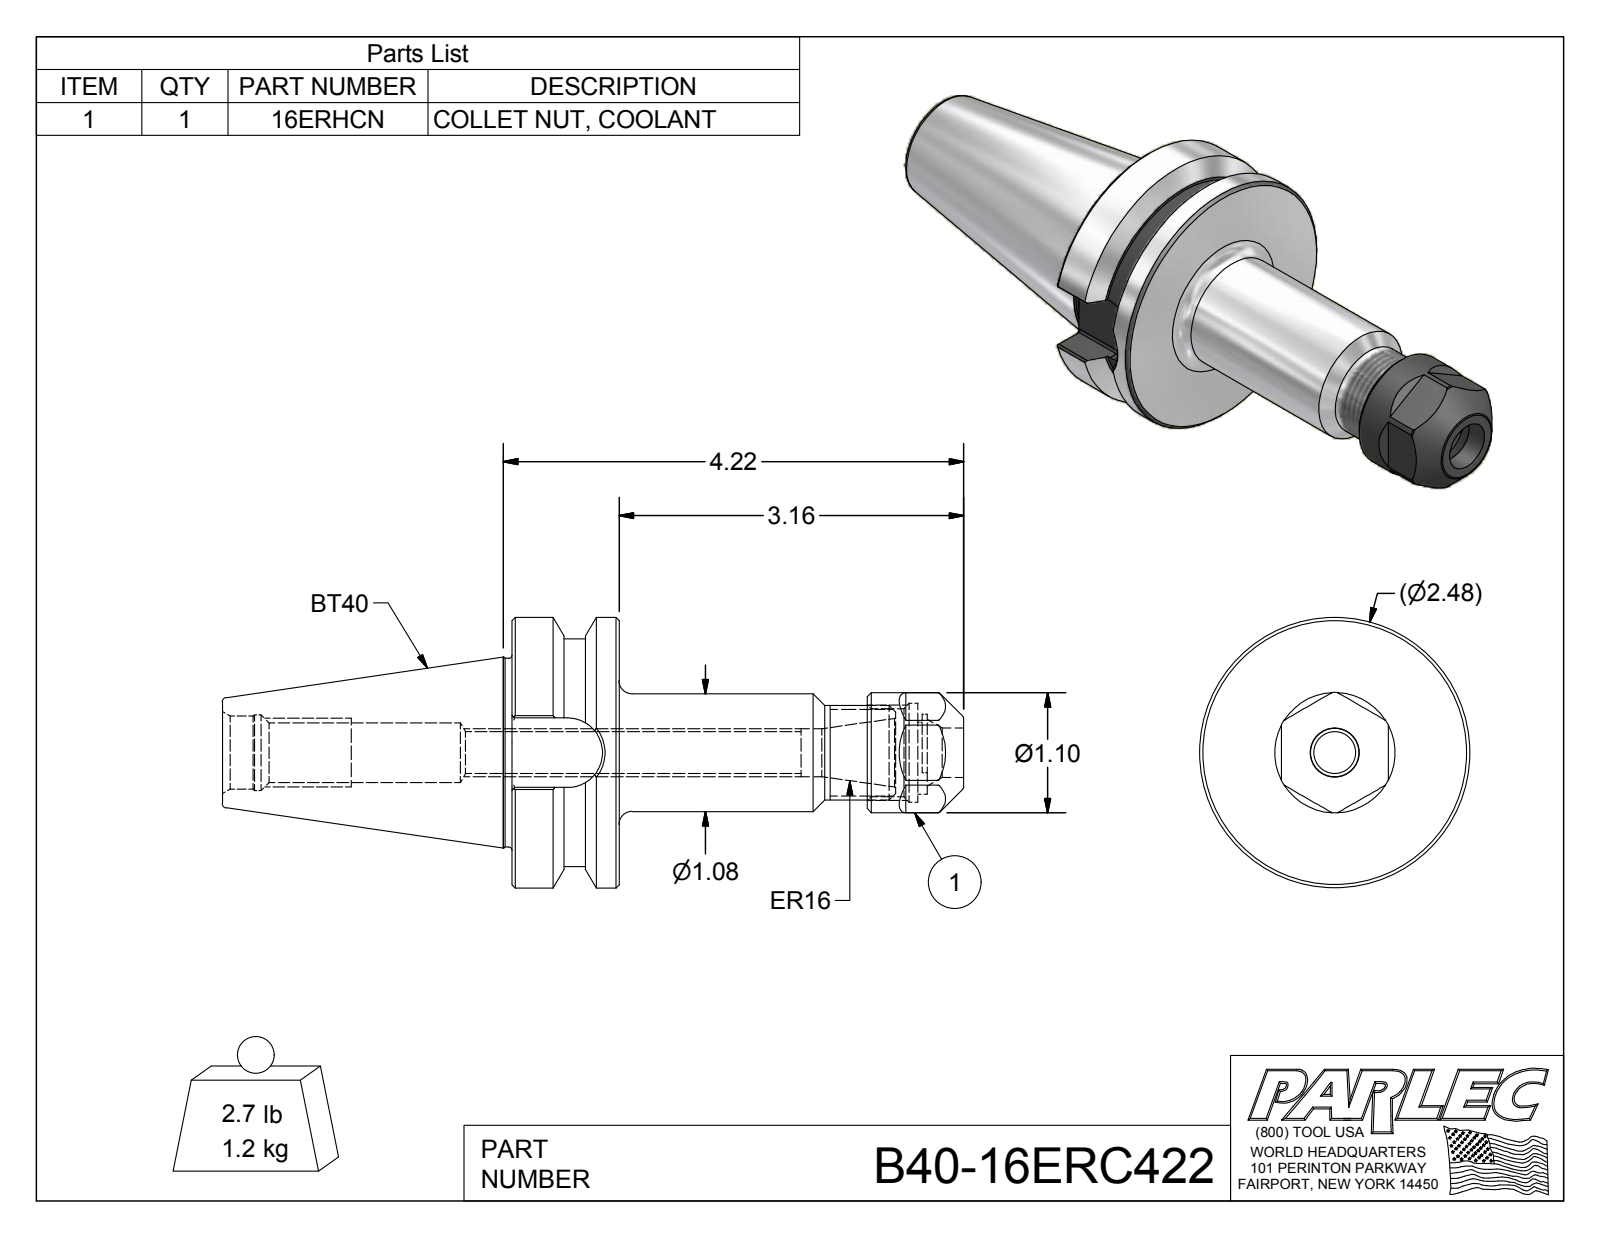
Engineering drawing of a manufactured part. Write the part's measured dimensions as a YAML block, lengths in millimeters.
part_name: "B40-16ERC422; B40-16ER4-1; 16ERHCN"
step_written_by: "Autodesk Inventor 2012 (AUTOMOTIVE_DESIGN)"
units: millimeters
bodies: {solids: 2, faces: 106, planar: 41, cylindrical: 29, other: 36}
overall_size: [172.6, 63, 63]
volume: 156400
surface_area: 32900
round_holes:
  - {diameter: 9.7, count: 1}
  - {diameter: 11.2, count: 1}
  - {diameter: 11.5, count: 1}
  - {diameter: 13.8, count: 1}
  - {diameter: 16.8, count: 1}
  - {diameter: 17, count: 1}
  - {diameter: 17.6, count: 1}
  - {diameter: 20.5, count: 1}
  - {diameter: 23, count: 1}
round_bosses_or_shafts:
  - {diameter: 63, count: 1}
  - {diameter: 53, count: 1}
  - {diameter: 43.9, count: 1}
  - {diameter: 28, count: 1}
  - {diameter: 27.4, count: 1}
  - {diameter: 22, count: 1}
partial_cylinders:
  - {radius: 0.5, count: 8}
  - {radius: 8.1, count: 1}
  - {radius: 9, count: 1}
face_to_face_distances: [25, 24.9, 45.2, 10.2, 35.1, 94.5, 69.5, 67.4, 92.4, 161.9]
hole_center_spacings: [1.3]
